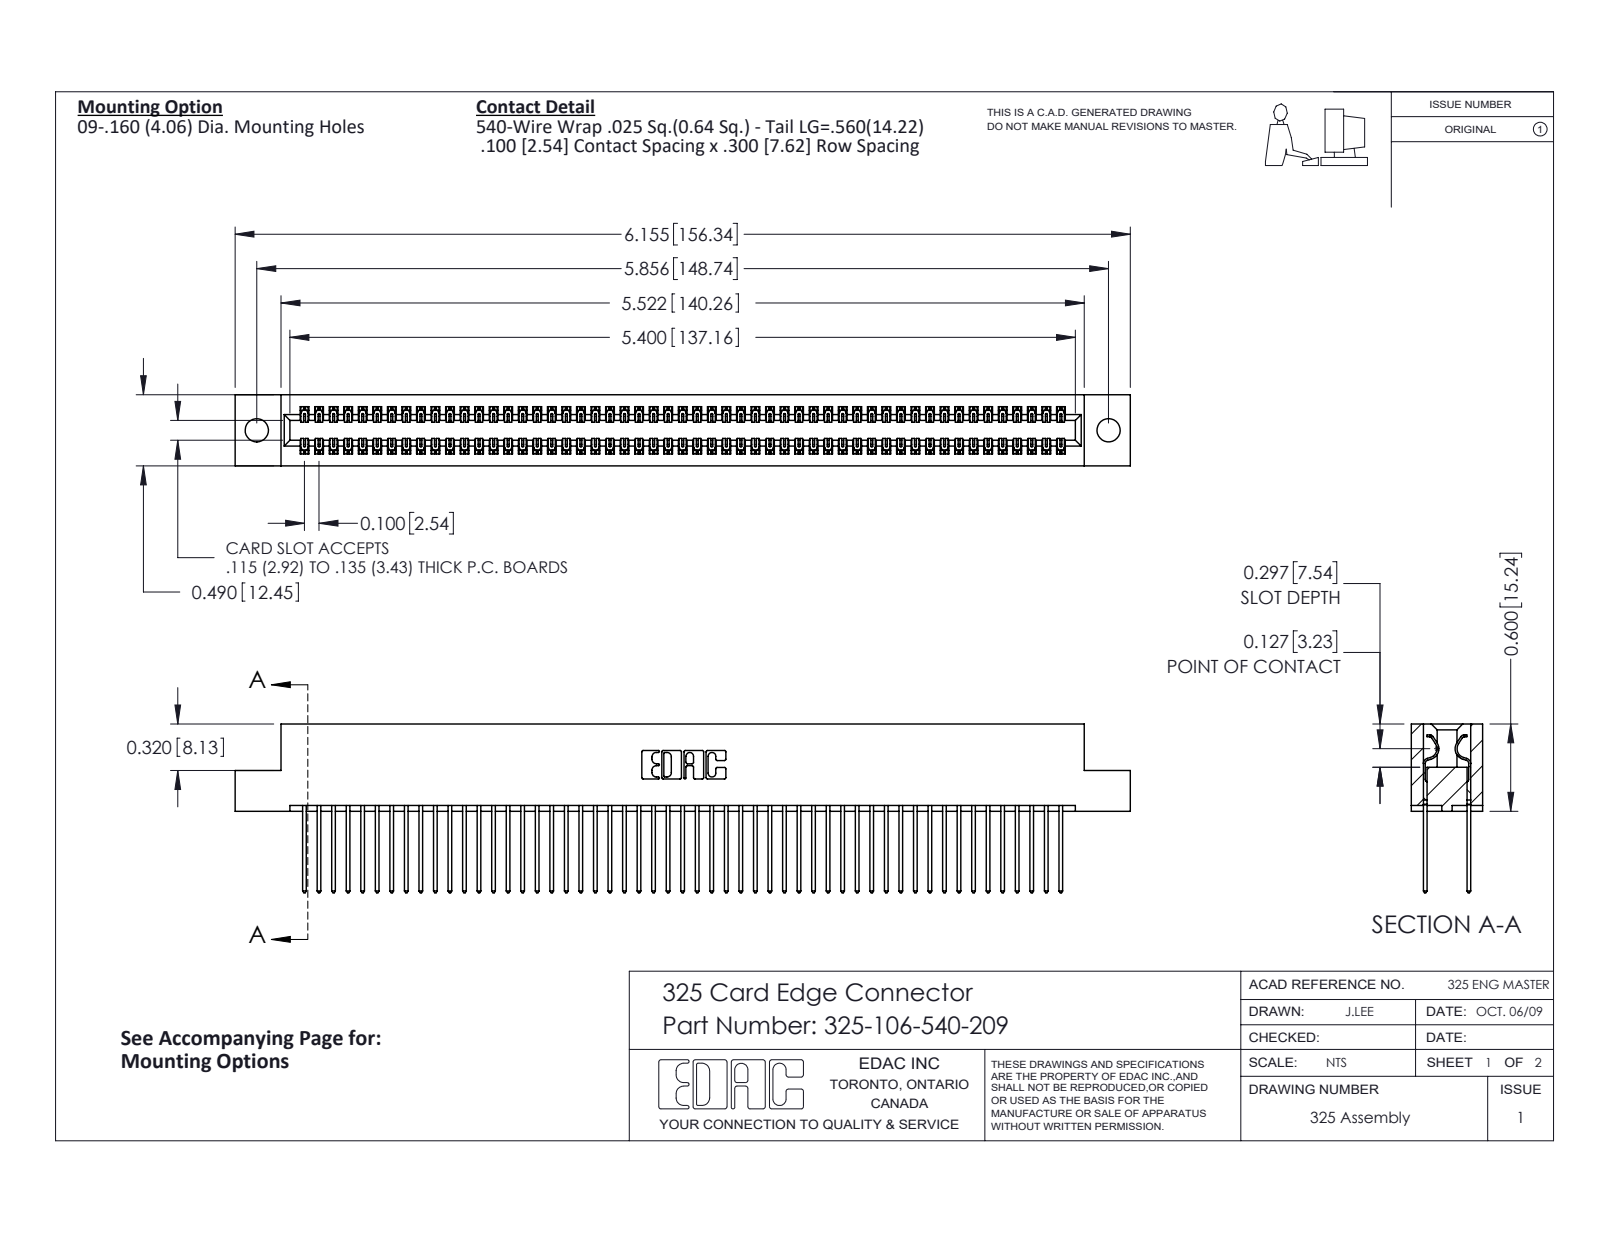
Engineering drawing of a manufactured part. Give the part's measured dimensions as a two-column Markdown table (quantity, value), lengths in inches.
| quantity | value |
| --- | --- |
| part name | 325-292-001_325-293-140; 325 Part_.160 TH; 325-106-540-209 |
| STEP written by | SolidWorks 2016 (CONFIG_CONTROL_DESIGN) |
| units | inches |
| bodies | 107 solids, 5626 faces (3886 planar, 1740 cylindrical, 0 other) |
| overall size | 6.155 × 1.16 × 0.49 |
| volume | 1.248 in³ |
| surface area | 41.62 in² |
| round holes (diameter × count) | 0.16 × 2 |
| partial cylindrical surfaces (radius × count) | 0.006 × 159, 0.01 × 106, 0.01 × 22, 0.007 × 6, 0.031 × 6, 0.026 × 3, 0.014 × 2, 0.022 × 2 |
| main face-to-face distances | 0.083, 0.407, 0.3, 0.107, 0.383, 0.025, 0.325, 0.49, 0.275, 0.56 |
| hole center spacings | 5.856 |
